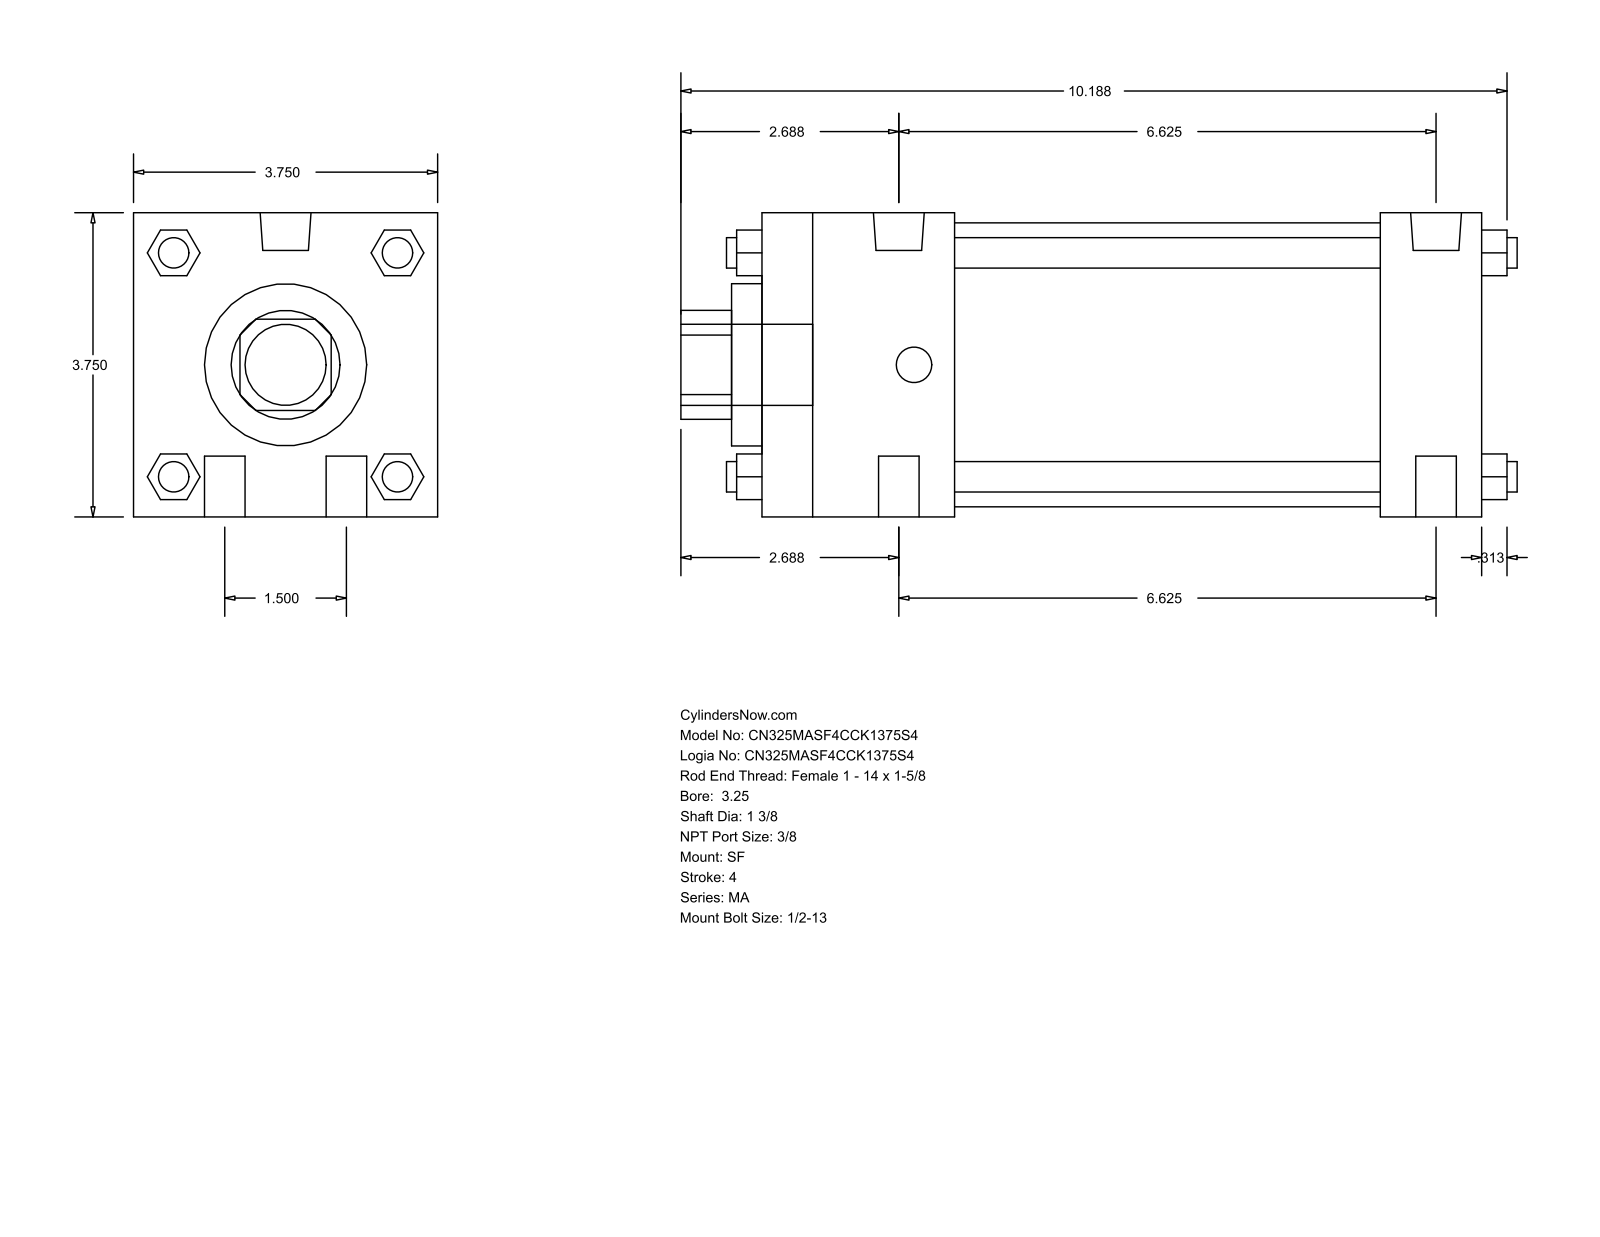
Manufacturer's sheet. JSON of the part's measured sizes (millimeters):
{"part_name": "MA_SF__0325_1.375", "step_written_by": "GSSL Pune (CONFIG_CONTROL_DESIGN)", "units": "millimeters", "bodies": {"solids": 0, "faces": 124, "planar": 94, "cylindrical": 30, "other": 0}, "overall_size": [261.94, 95.25, 95.25], "round_holes": [[34.92, 1], [50.8, 1], [88.9, 1]], "round_bosses_or_shafts": [[12.7, 4], [9.53, 4], [15.93, 2], [11.11, 2], [25.4, 1]], "partial_cylinders_radius": [[17.06, 1]], "face_to_face_distances": [95.24, 225.42, 193.67, 31.75, 60.32, 133.35, 165.1, 9.52, 69.84, 203.19]}
